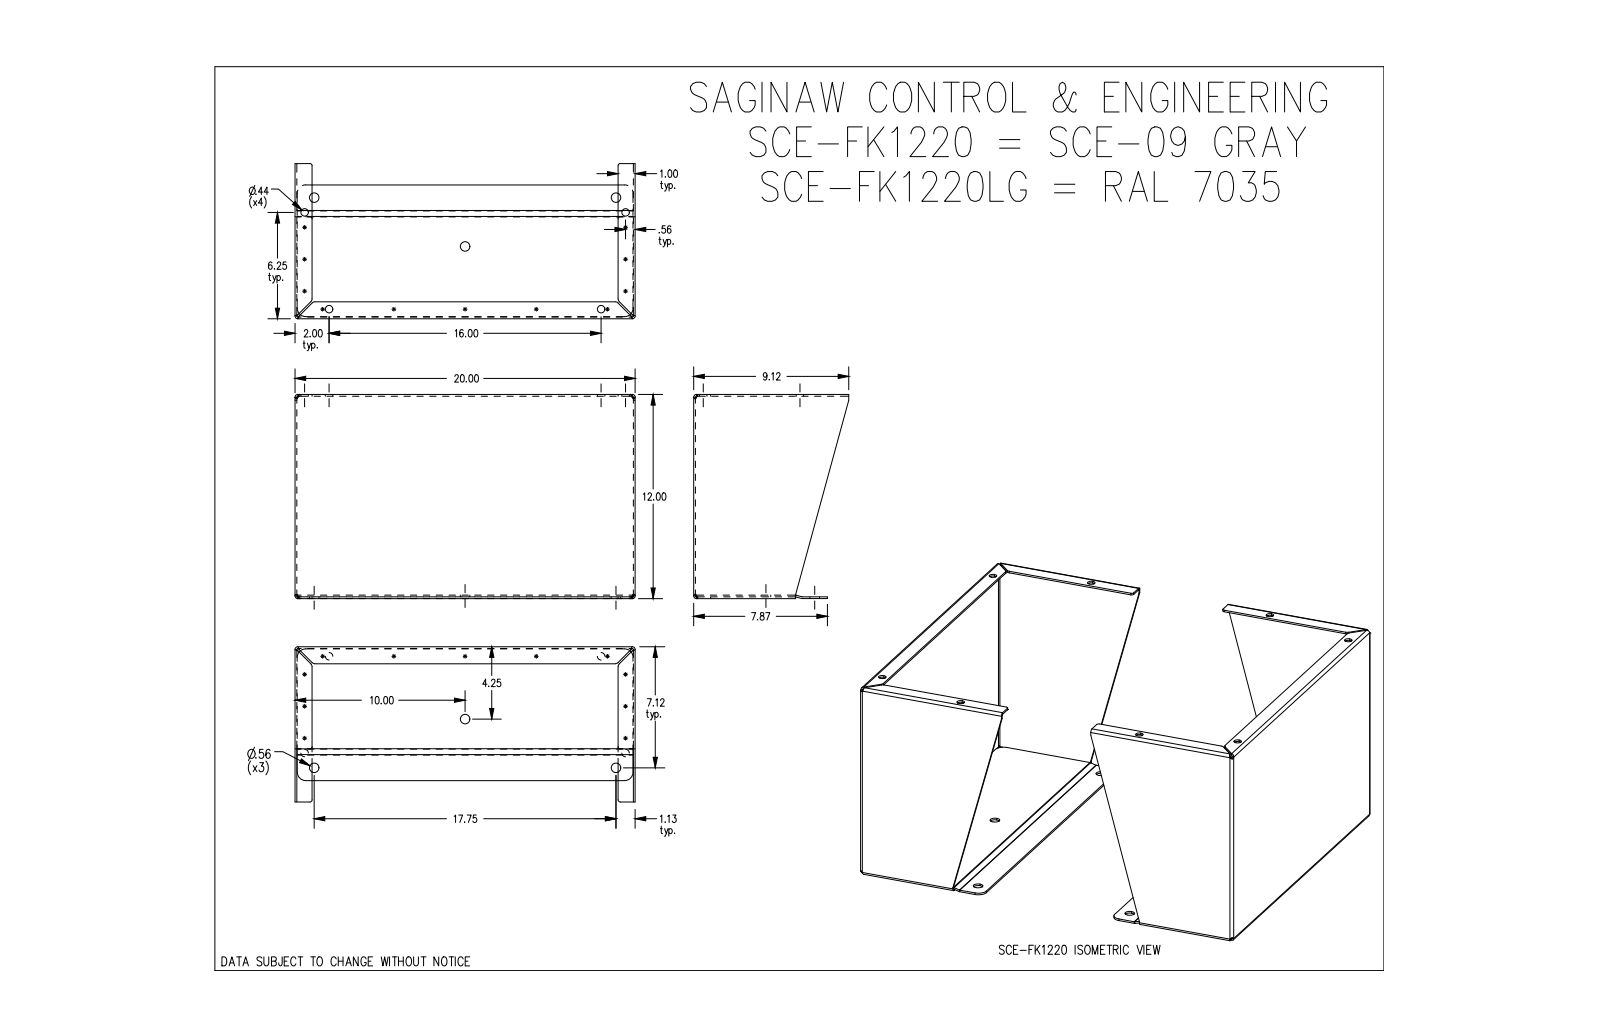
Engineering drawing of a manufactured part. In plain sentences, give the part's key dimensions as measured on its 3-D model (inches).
The part is named "SCE-FK1220". Its 3-D file was written by "SolidWorks 2019 (CONFIG_CONTROL_DESIGN)". It is 4 solids with 214 faces: 96 planar, 86 cylindrical and 32 other. Overall it measures 24 by 20 by 12 inches. Its volume is 129.9 cubic inches and its surface area 2 533 square inches. Round holes: 8 of diameter 0.437, 6 of diameter 0.563. Partial cylindrical surfaces (rounded edges, fillets, slot ends): 16 of radius 0.166, 10 of radius 0.062, 9 of radius 0.063, 8 of radius 0.125, 8 of radius 0.22, 8 of radius 0.5. The main face-to-face distances are 0.104, 23.896, 19.896, 24, 23.792, 20, 19.792, 11.792, 0.101, 11.893. The hole center spacings are 1.035, 5.866, 6.614, 8.809, 9.647, 10.646, 16.343, 16.47.
